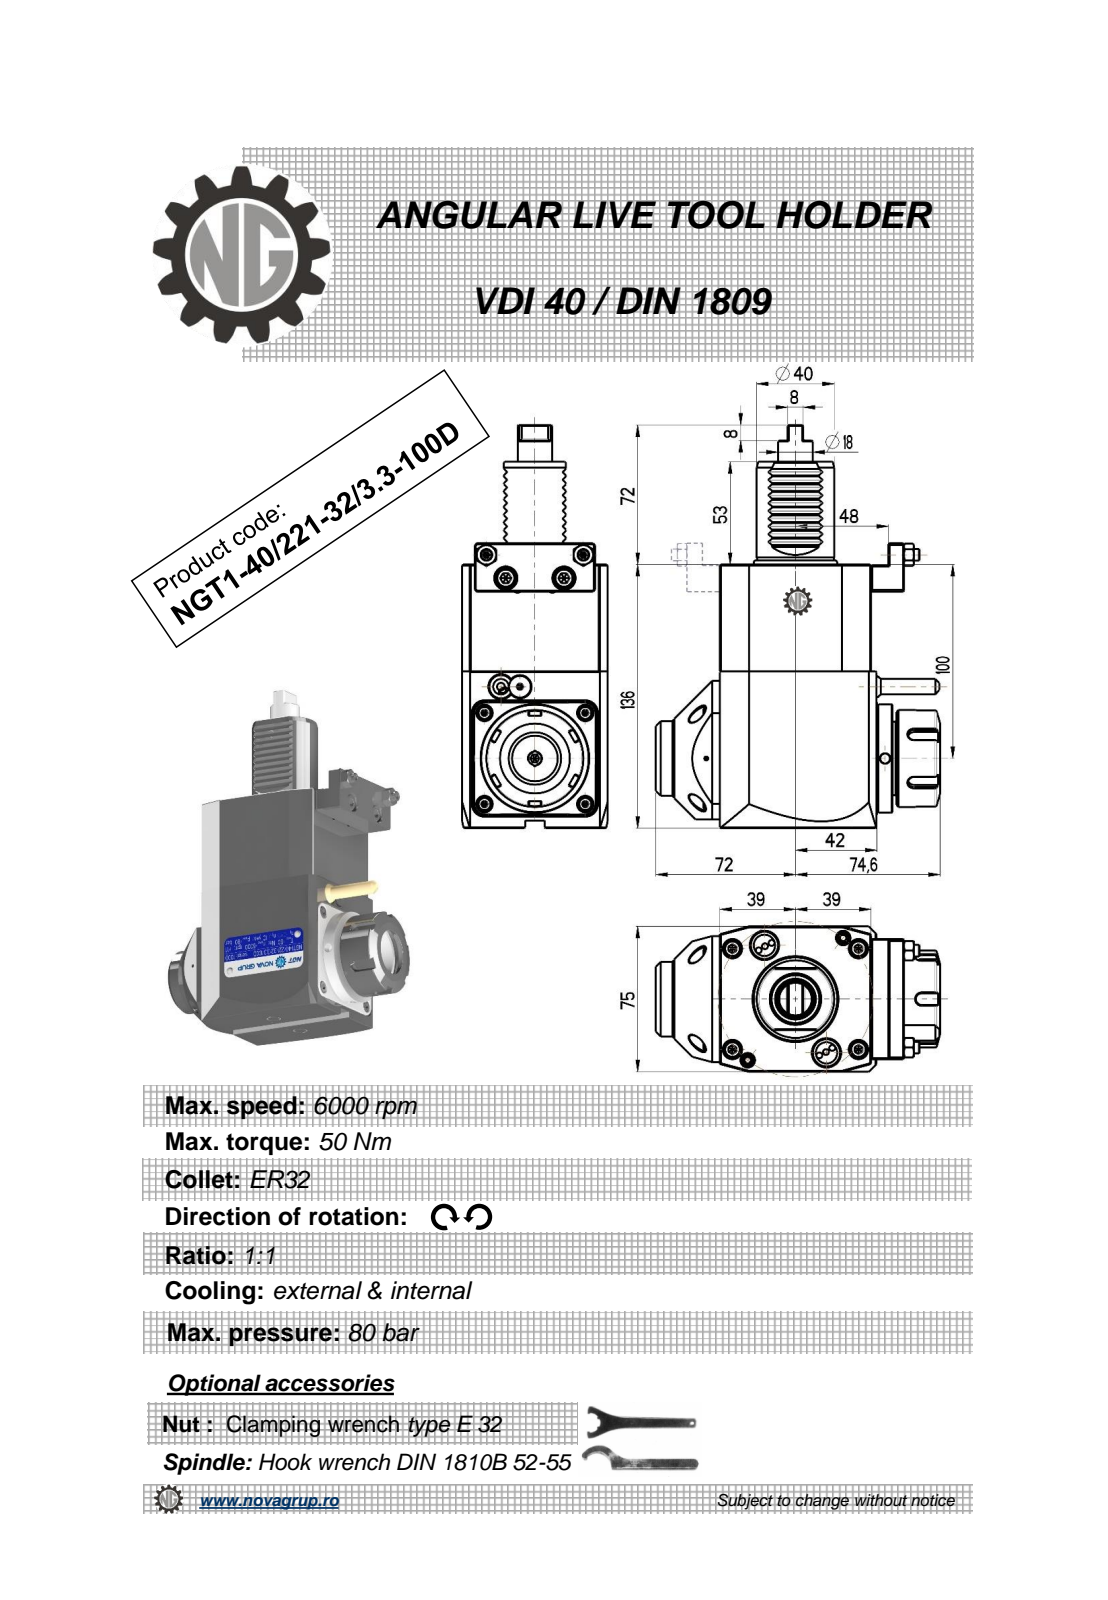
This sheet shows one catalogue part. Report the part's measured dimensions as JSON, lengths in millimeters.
{"part_name": "NGT1_40_221_32_3_3_100D", "step_written_by": "PRO/ENGINEER BY PARAMETRIC TECHNOLOGY CORPORATION, 2010280 (CONFIG_CONTROL_DESIGN)", "units": "millimeters", "bodies": {"solids": 1, "faces": 443, "planar": 210, "cylindrical": 88, "other": 145}, "overall_size": [208, 146.6, 75], "volume_mm3": 1025000, "surface_area_mm2": 80776, "round_holes": [[5, 3], [3, 1], [27, 1], [42, 1]], "round_bosses_or_shafts": [[6, 2], [56, 1], [50, 1], [41.4, 1], [41, 1], [40, 1], [38.5, 1], [17.8, 1]], "partial_cylinders_radius": [[0.3, 20], [0.31, 10], [0.22, 6], [3, 5], [0.8, 2], [40, 1]], "face_to_face_distances": [75, 136, 78, 14, 81, 0.5, 11, 3, 8, 122], "hole_center_spacings": [40.93]}
